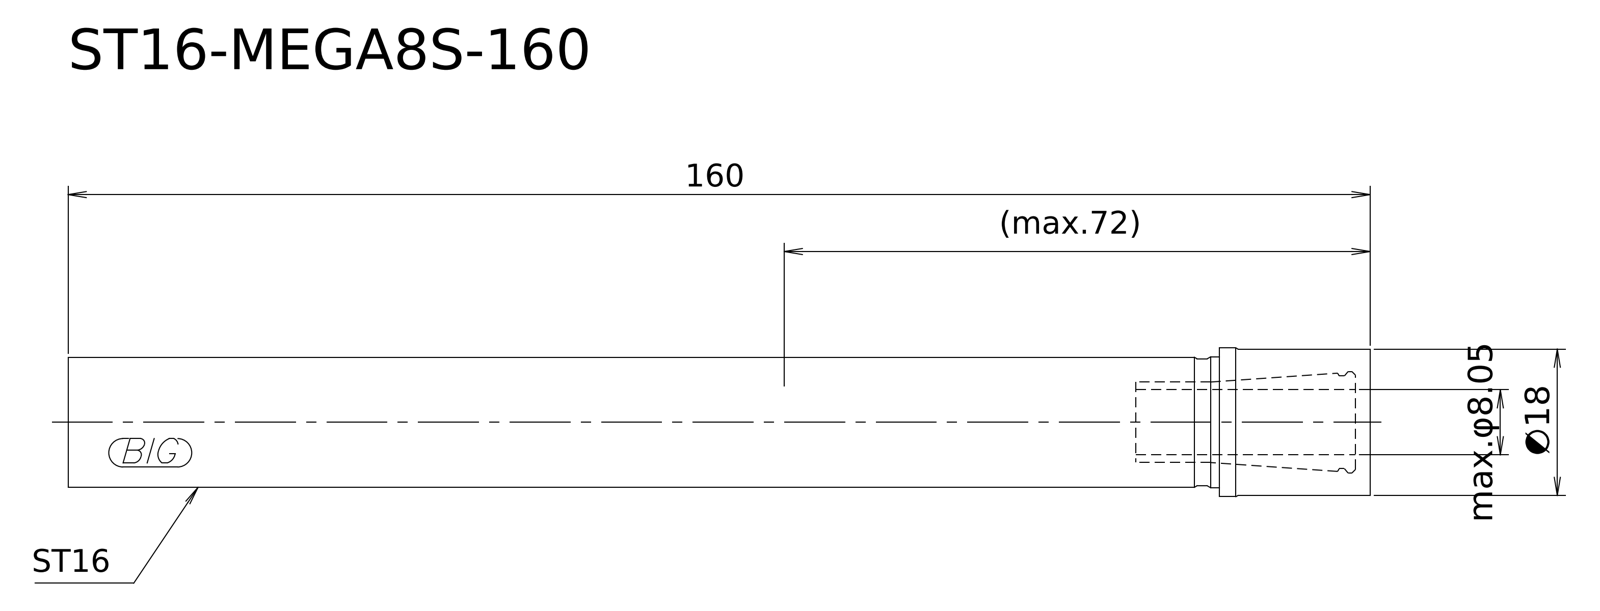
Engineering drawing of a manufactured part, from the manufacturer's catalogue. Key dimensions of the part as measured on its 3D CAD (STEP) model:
STEP written by: Kubotek KeyCreator V8.5.1 (14335) (CONFIG_CONTROL_DESIGN)
Units: millimetres
Bodies: 1 solid, 7 faces (3 planar, 3 cylindrical, 1 other)
Overall size (bounding box): 160 × 18.3 × 18.3
Volume: 33 180 mm³ · Surface area: 8 679 mm²
Round bosses / shafts (diameter × count): ⌀18.3 ×1, ⌀18 ×1, ⌀16 ×1
Main face-to-face distances: 160, 18.5, 141.5
